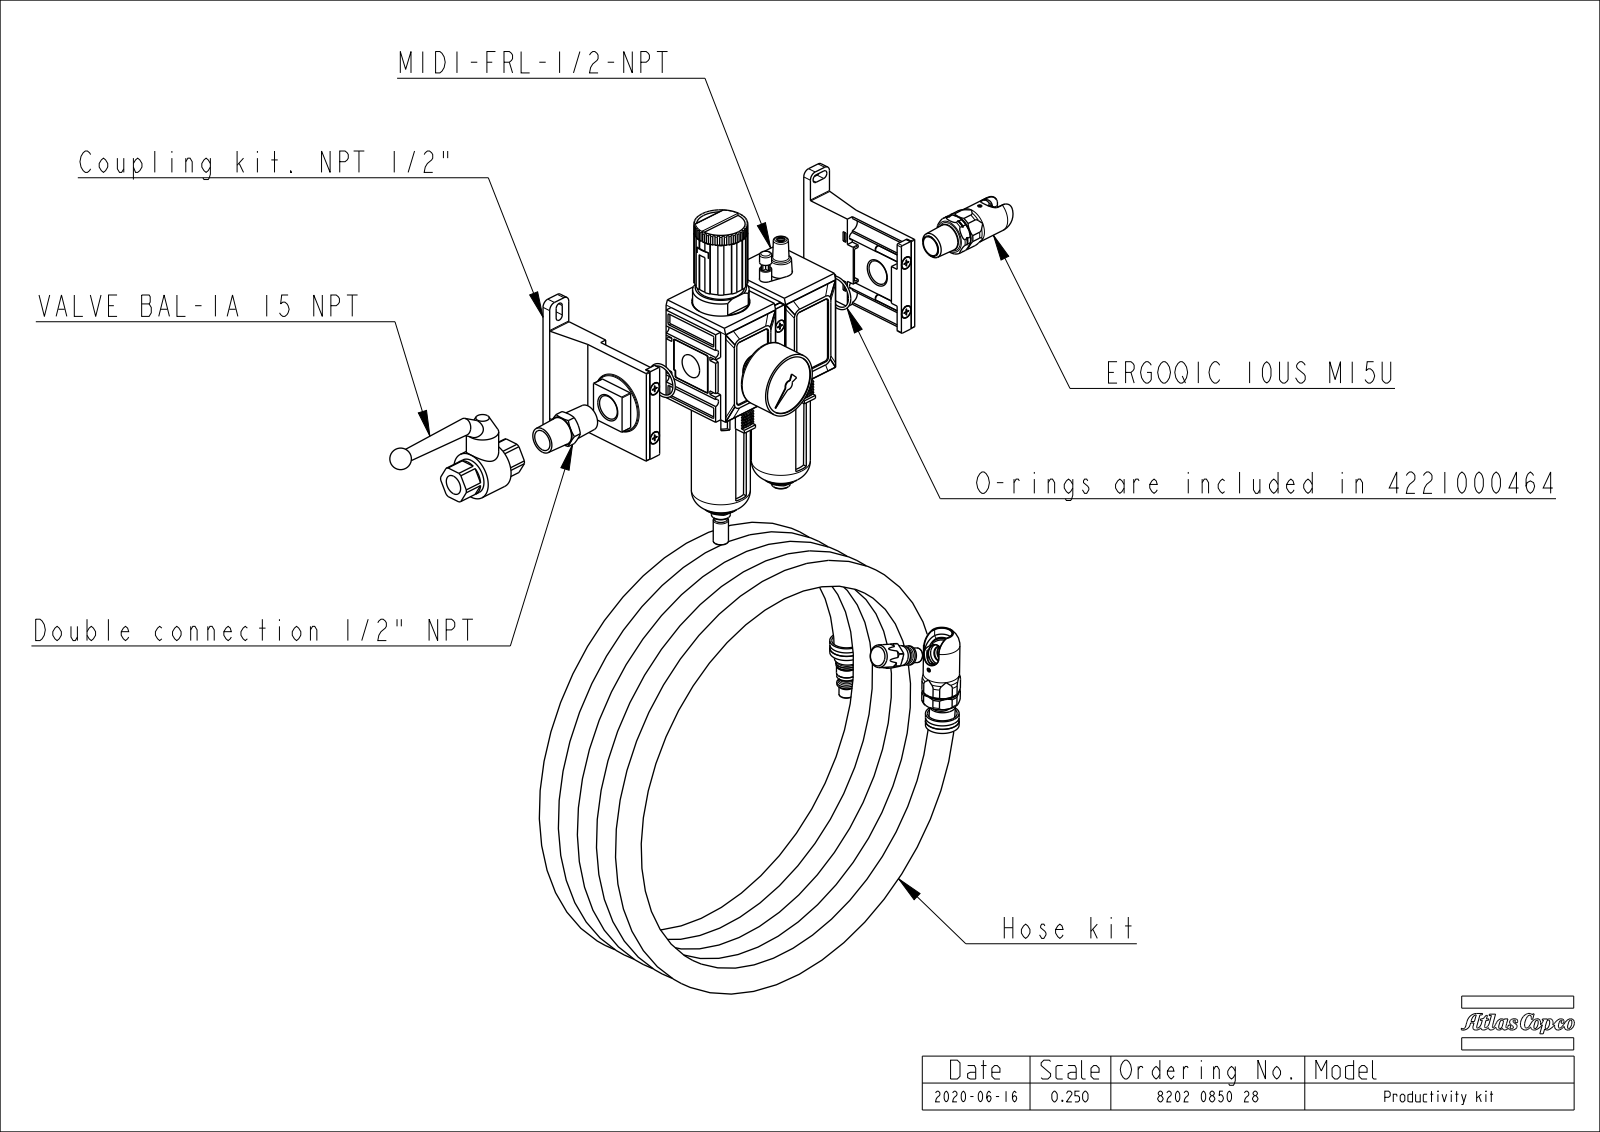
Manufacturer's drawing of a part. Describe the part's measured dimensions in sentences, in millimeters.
The part is named "4221000166; 4221000186_IMP1; 4221000186_IMP3; 4221000186_IMP2 (+8 more)". Its 3-D file was written by "CREO PARAMETRIC BY PTC INC, 2018100 (CONFIG_CONTROL_DESIGN)". It is 35 solids with 2388 faces: 926 planar, 683 cylindrical and 779 other. Overall it measures 640.69 by 392.12 by 143.5 millimeters. Its volume is 2 112 000 cubic millimeters and its surface area 767 328 square millimeters. Round holes: 6 of diameter 5.2, 6 of diameter 6, 4 of diameter 4.13, 4 of diameter 8, 2 of diameter 2, 2 of diameter 2.05, 2 of diameter 8.3, 2 of diameter 8.57, 2 of diameter 9.6, 2 of diameter 10.9, 2 of diameter 14, 2 of diameter 14.4. Round bosses or shafts: 6 of diameter 9.3, 6 of diameter 5, 6 of diameter 4.51, 4 of diameter 27, 4 of diameter 24, 3 of diameter 23, 3 of diameter 14.65, 2 of diameter 43.8. Partial cylindrical surfaces (rounded edges, fillets, slot ends): 60 of radius 1, 43 of radius 0.25, 22 of radius 0.5, 8 of radius 3.2, 8 of radius 5, 6 of radius 5.2, 4 of radius 1.65, 4 of radius 7.55. The main face-to-face distances are 5.2, 120.8, 14, 8.8, 129.6, 134.8, 5, 2, 80, 126. The hole center spacings are 63, 6.9, 37.86, 75.72, 42, 96.81, 126, 132.82.
